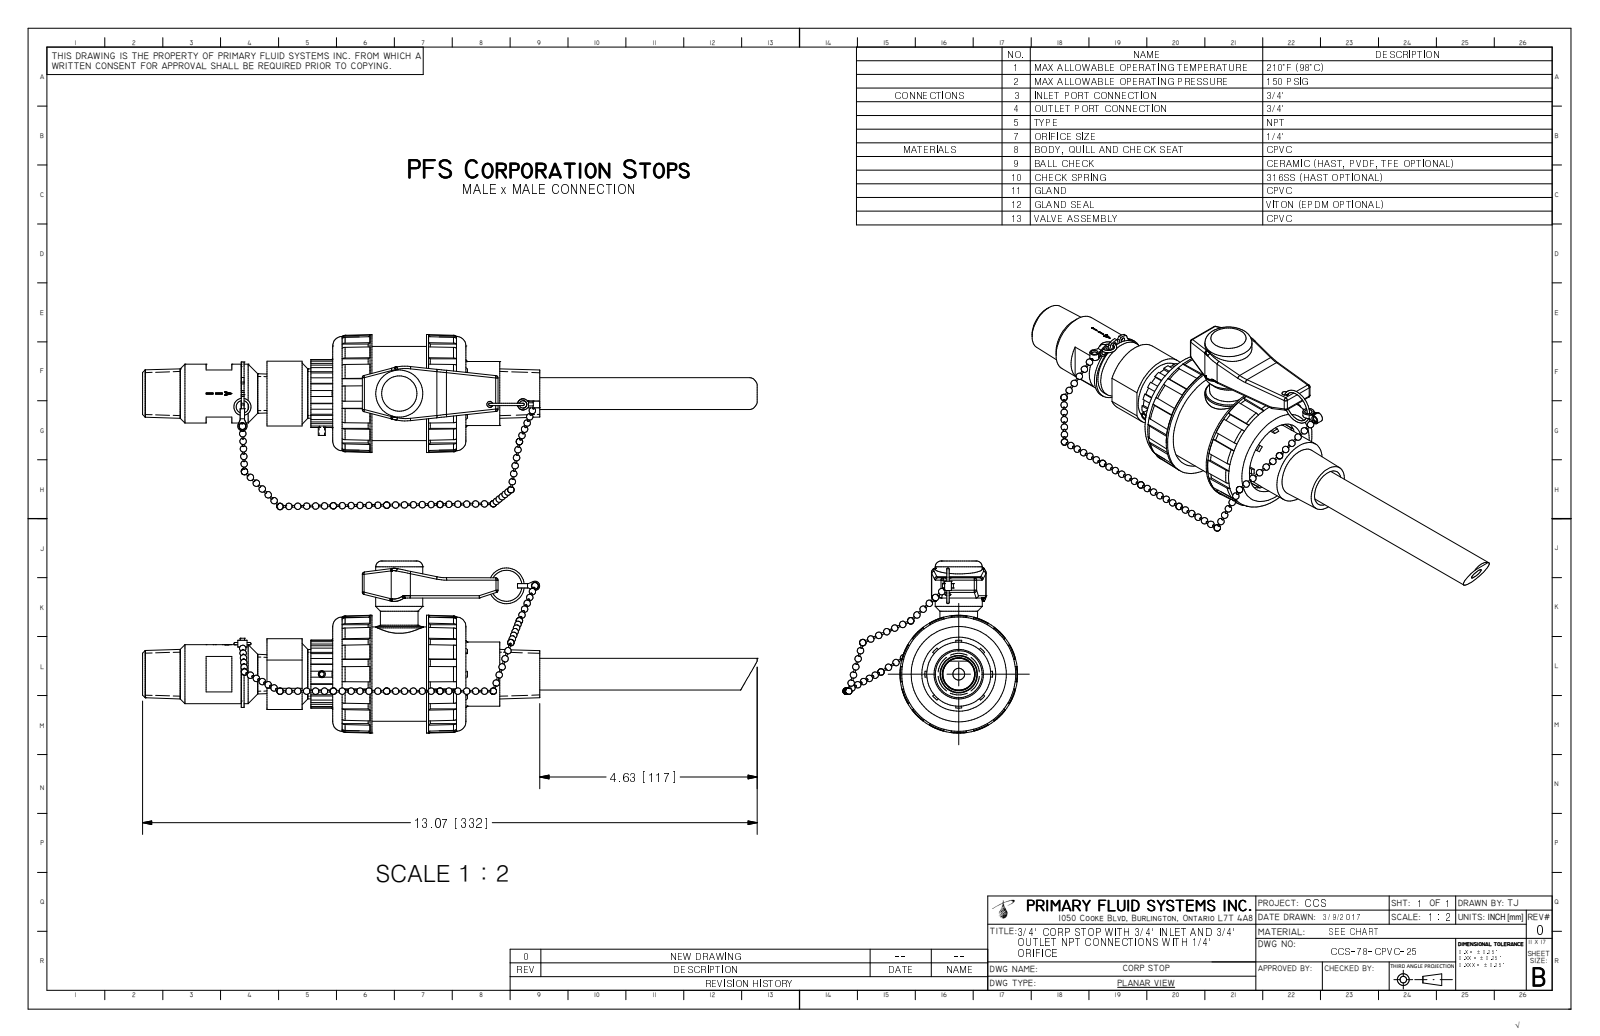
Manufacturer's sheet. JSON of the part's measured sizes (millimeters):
{"part_name": "CCS-78-CPVC-25_R0", "step_written_by": "Autodesk Inventor 2009 (AUTOMOTIVE_DESIGN)", "units": "millimeters", "bodies": {"solids": 1, "faces": 615, "planar": 225, "cylindrical": 144, "other": 246}, "overall_size": [332, 94.3, 92.7], "volume_mm3": 326100, "surface_area_mm2": 73420, "round_holes": [[2.5, 1], [6.4, 1], [11.9, 1], [14.2, 1], [39.9, 1], [54.9, 1]], "round_bosses_or_shafts": [[63.5, 1], [50.8, 1], [45.7, 1], [34.5, 1], [34.1, 1], [31.8, 1], [29, 1], [25.4, 1]], "partial_cylinders_radius": [[1.3, 21], [25.4, 3], [1.4, 2], [5, 2], [8.9, 1], [15.8, 1], [18.3, 1], [19.1, 1]], "face_to_face_distances": [5.2, 66.7, 21.2, 50.7, 16, 45.5, 11.8, 71.9, 61.5, 29.5], "hole_center_spacings": [16.7]}
